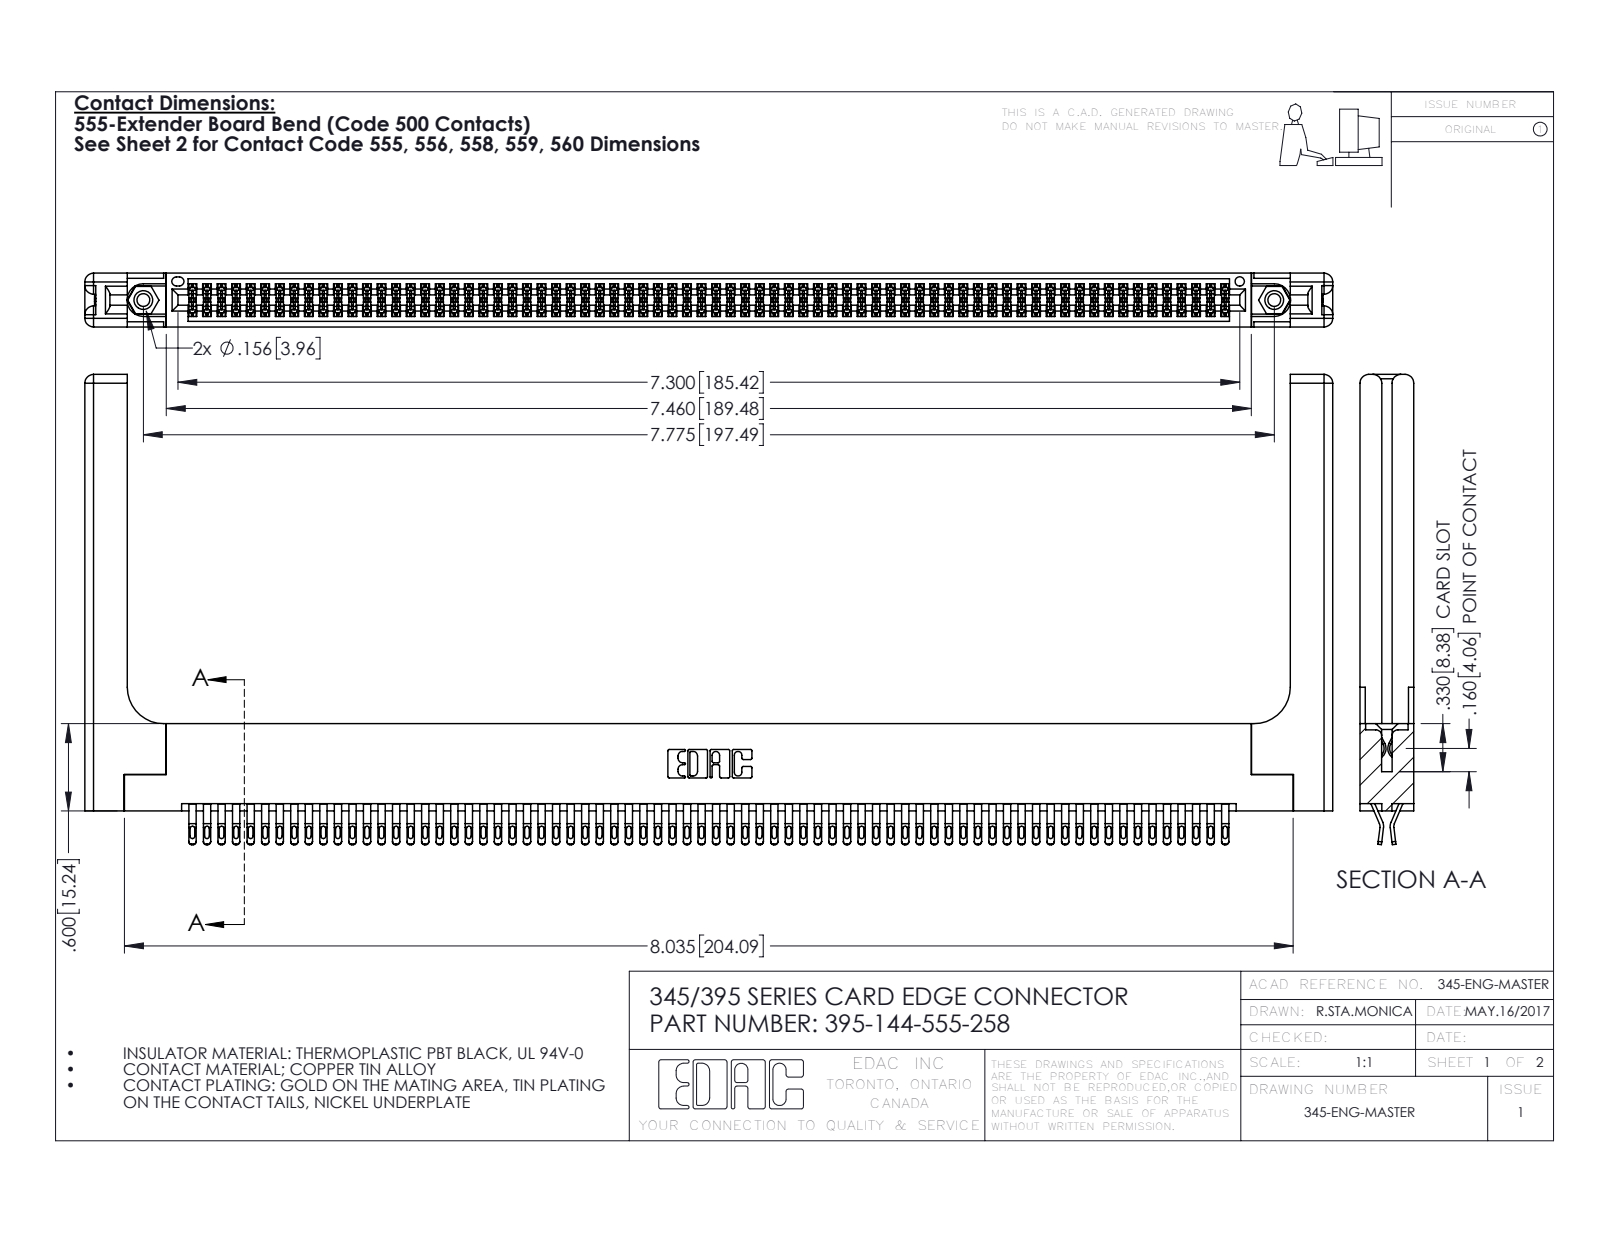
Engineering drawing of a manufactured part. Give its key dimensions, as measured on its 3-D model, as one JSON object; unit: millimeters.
{"part_name": "395-144-555-258; 345-292-001_555 Tail; 345-250-001_345-250-001-102; 345 Part_Flush Mounting Lugs - 0.156 Dia-TH (+1 more)", "step_written_by": "SolidWorks 2016 (CONFIG_CONTROL_DESIGN)", "units": "millimeters", "bodies": {"solids": 149, "faces": 8446, "planar": 4692, "cylindrical": 3694, "other": 60}, "overall_size": [217.9, 82.1, 9.4], "volume_mm3": 30330, "surface_area_mm2": 39410, "round_holes": [[2.3, 2], [3.2, 2], [4, 2], [1.6, 1]], "round_bosses_or_shafts": [[3.9, 2]], "partial_cylinders_radius": [[0.4, 360], [0.5, 288], [0.2, 216], [0.3, 22], [1.5, 16], [0.2, 6], [0.8, 6], [0.7, 3]], "face_to_face_distances": [1.8, 7.6, 9.4, 0.6, 5.1, 2.5, 6.9, 5.7, 4.4, 3.8], "hole_center_spacings": [6.9, 191.5, 197.5]}
